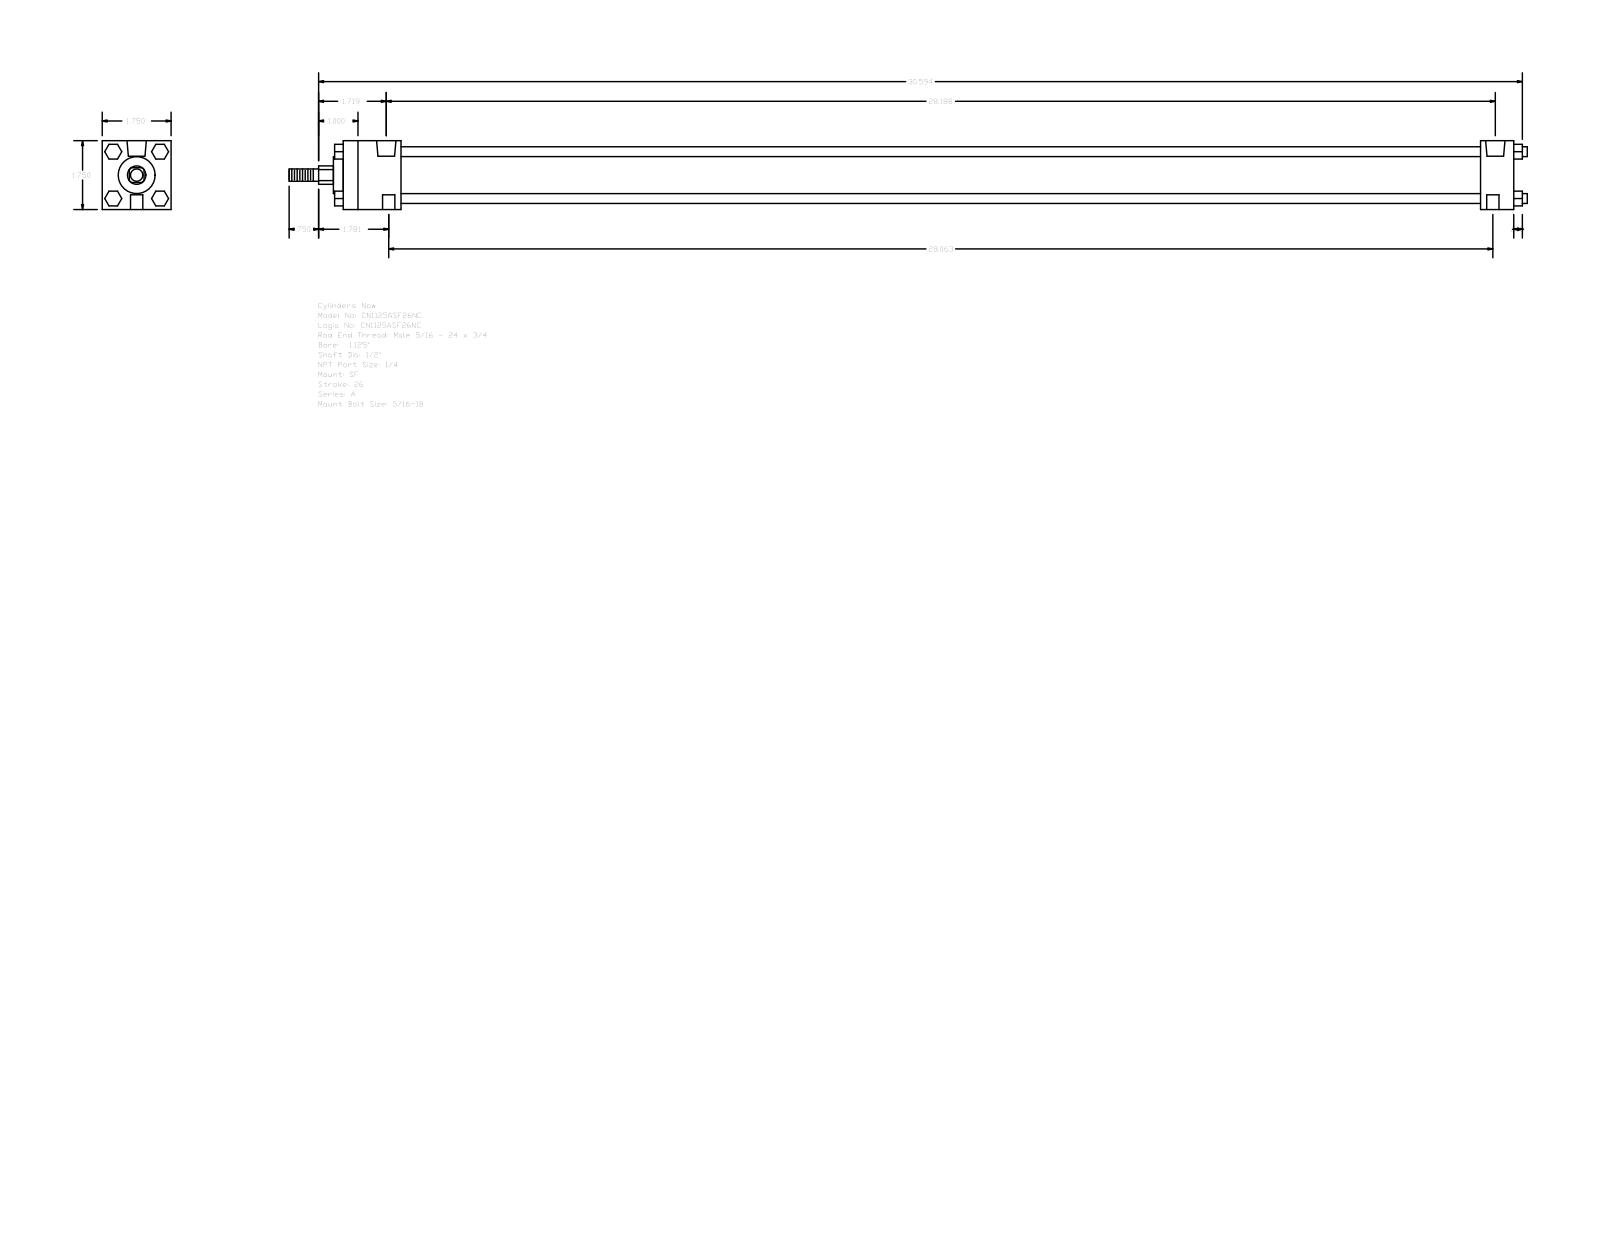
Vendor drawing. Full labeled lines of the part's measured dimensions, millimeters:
Part name (STEP PRODUCT): A_SF__0112_0.5
STEP written by: GSSL Pune (CONFIG_CONTROL_DESIGN)
Units: millimetres
Bodies: 0 solids, 120 faces (92 planar, 28 cylindrical, 0 other)
Overall size (bounding box): 799.31 × 44.45 × 44.45
Round holes (diameter × count): ⌀5.56 ×2, ⌀7.94 ×2, ⌀12.49 ×2
Round bosses / shafts (diameter × count): ⌀6.35 ×4, ⌀31.88 ×1, ⌀23.81 ×1, ⌀12.7 ×1, ⌀7.94 ×1
Partial cylindrical surfaces — rounded edges, fillets, slot ends (radius × count): R5.94 ×1
Main face-to-face distances: 44.46, 755.64, 734.21, 21.43, 37.3, 696.91, 718.34, 9.53, 5.59, 5.56
Hole centre spacings: 712.79, 1.58, 1.59, 714.37, 714.38, 715.96
